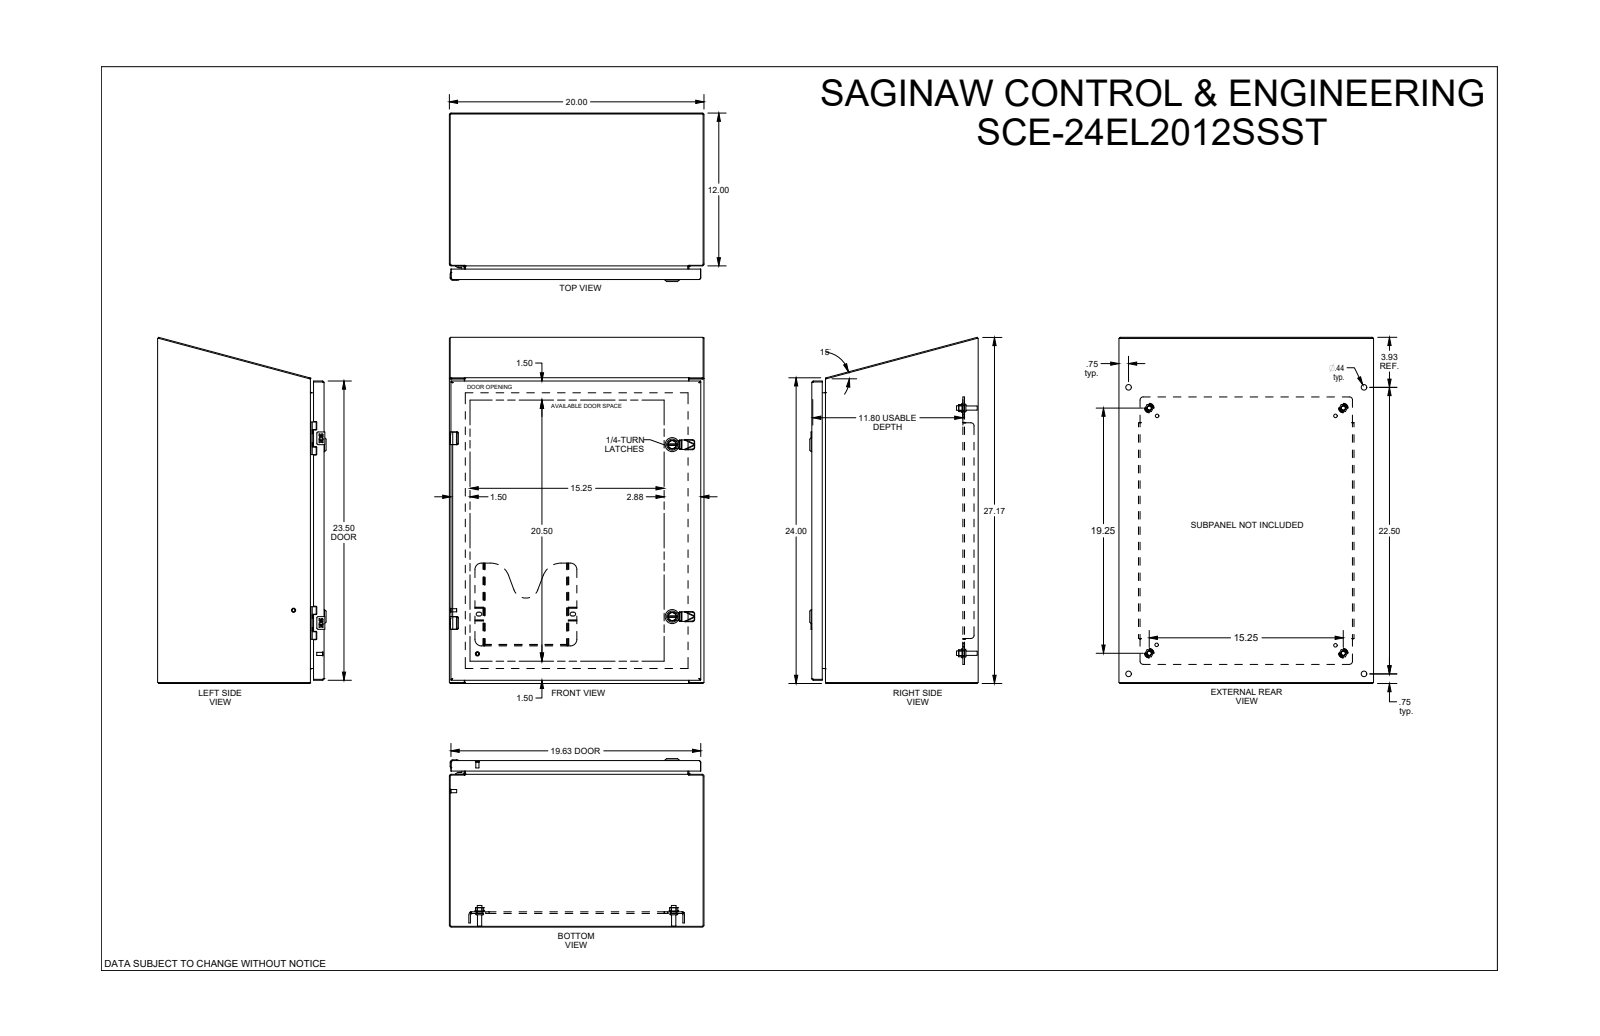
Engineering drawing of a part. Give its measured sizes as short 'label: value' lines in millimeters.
name: SCE-24EL2012SSST
written by: SolidWorks 2019 (CONFIG_CONTROL_DESIGN)
unit: mm
bodies: 0 solids, 2812 faces (1301 planar, 749 cylindrical, 762 other)
size: 690.3 × 508 × 336
holes: 4× ⌀4.4, 4× ⌀5.2, 4× ⌀6.2, 4× ⌀6.8, 4× ⌀7.1, 4× ⌀9.3, 4× ⌀11.1, 4× ⌀12.7, 2× ⌀4, 2× ⌀5, 2× ⌀5.5, 2× ⌀6.4
bosses: 6× ⌀4.3, 4× ⌀9.3, 4× ⌀8.4, 4× ⌀6.4, 4× ⌀6.3, 3× ⌀5, 2× ⌀28, 2× ⌀22
rounds: 56× R0.3, 32× R0.4, 28× R0.3, 23× R1, 20× R0.5, 12× R0.7, 11× R1.5, 10× R1.8
face distances: 1.9, 1.9, 506.1, 330.1, 328.2, 332.1, 330.1, 3.2, 25.4, 302.8
hole spacings: 368.3, 25, 0.5, 58.4, 114.1, 430.6, 531.8, 681.8
